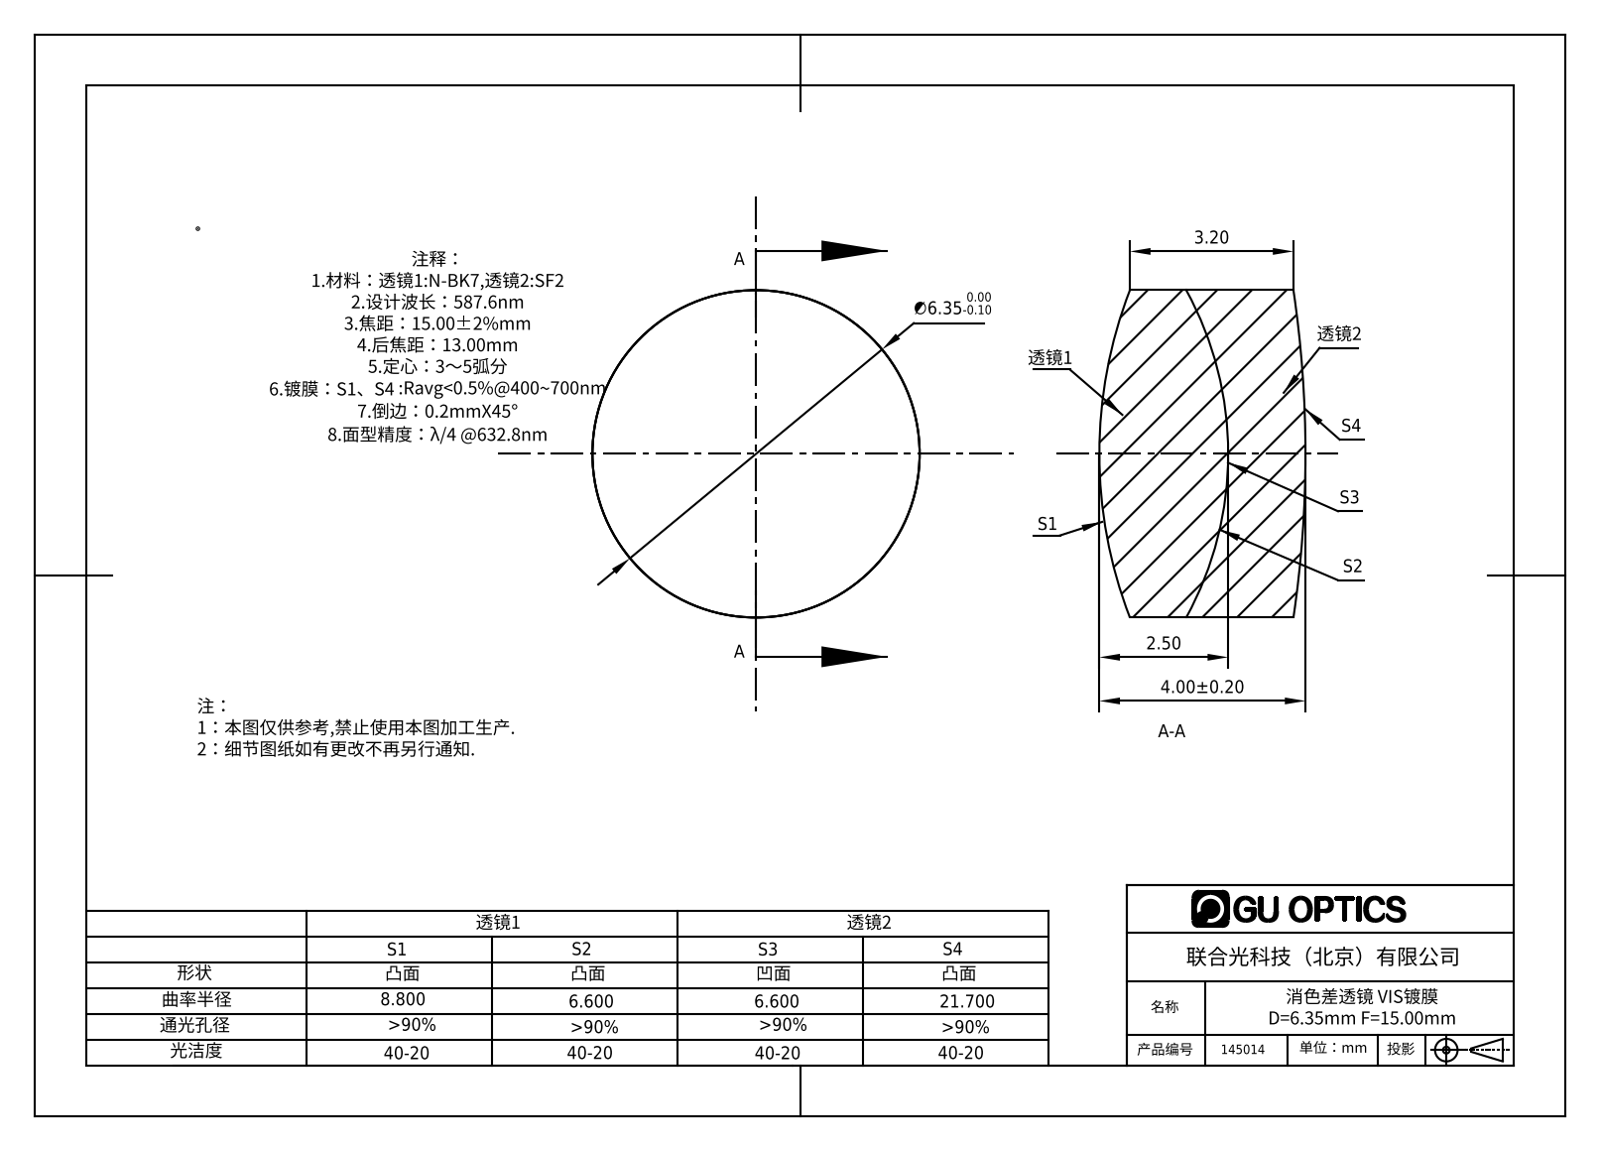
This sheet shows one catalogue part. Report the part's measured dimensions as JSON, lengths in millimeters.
{"part_name": "145014", "step_written_by": "SolidWorks 2016 (AUTOMOTIVE_DESIGN)", "units": "millimeters", "bodies": {"solids": 2, "faces": 12, "planar": 0, "cylindrical": 4, "other": 8}, "overall_size": [6.35, 6.35, 4], "volume_mm3": 114, "surface_area_mm2": 195, "round_bosses_or_shafts": [[6.35, 1]]}
